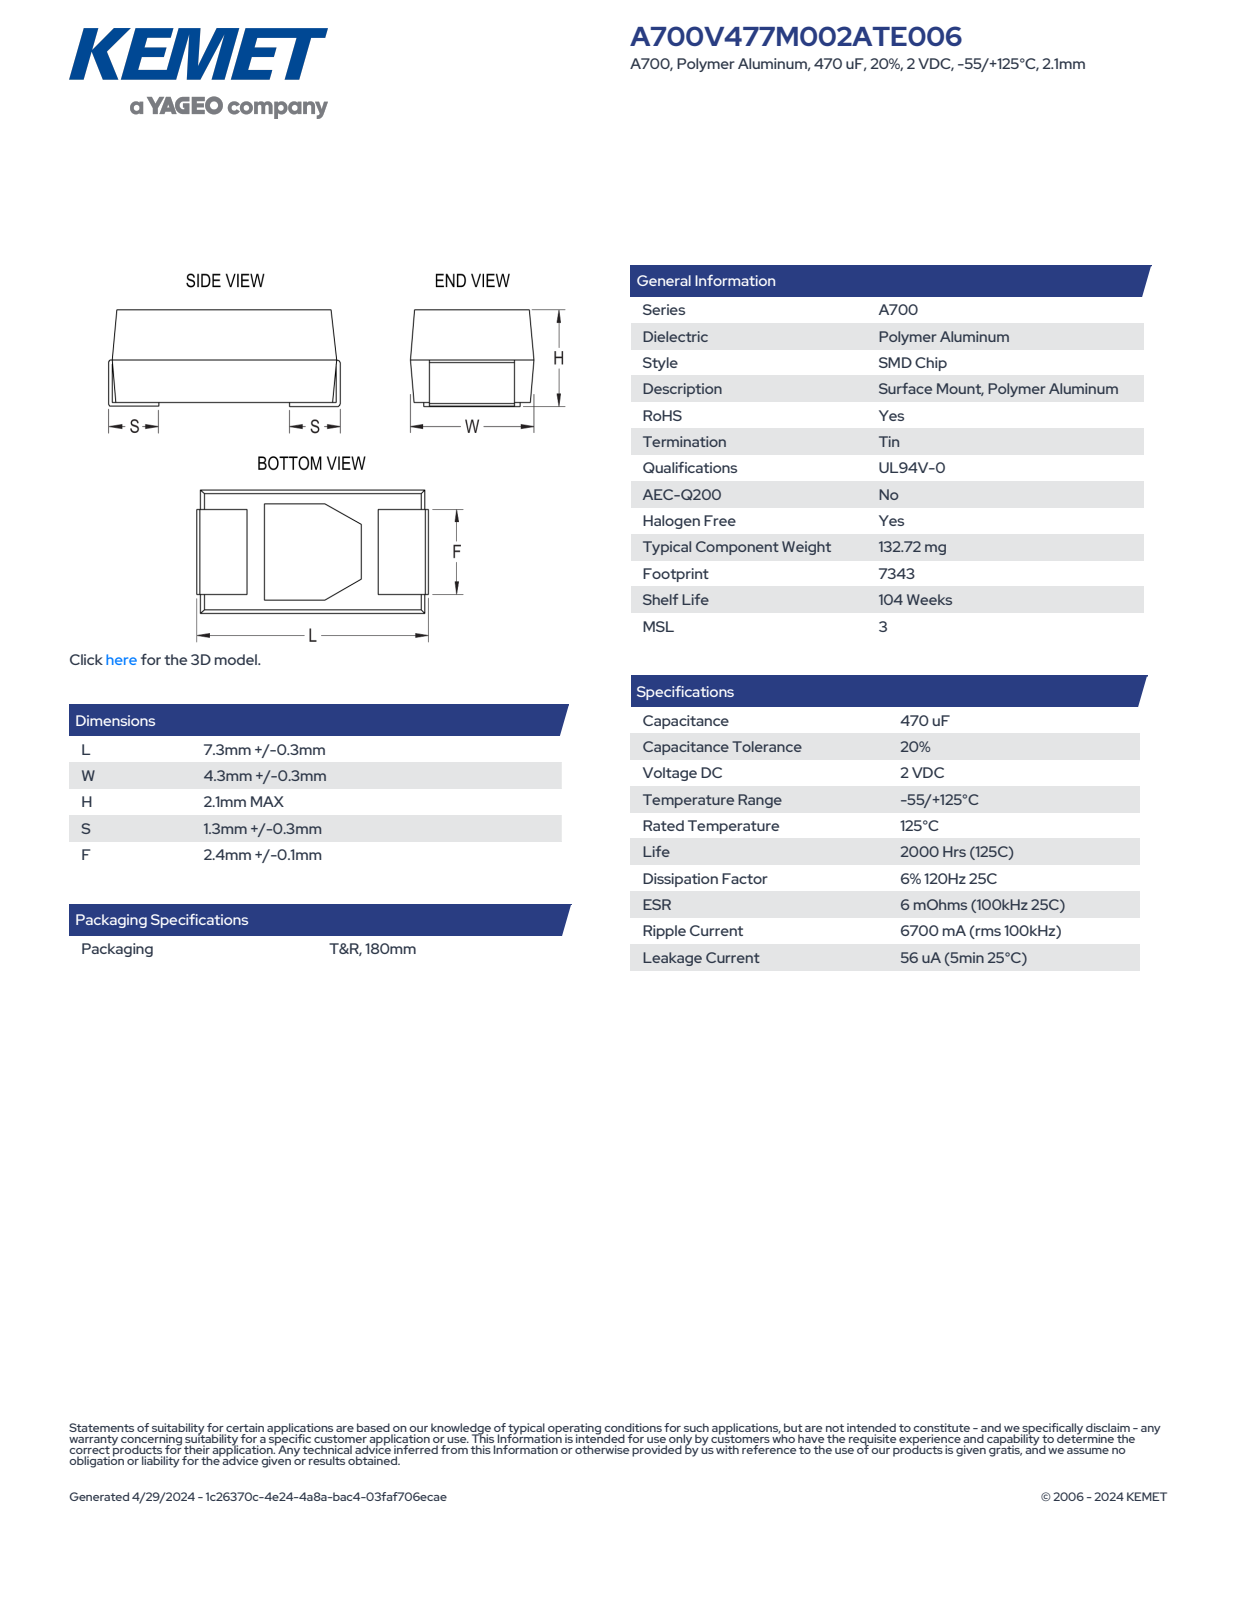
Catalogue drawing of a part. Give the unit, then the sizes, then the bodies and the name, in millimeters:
Units: millimetres
Overall size (bounding box): 7.6 × 4.6 × 2.1
Partial cylindrical surfaces — rounded edges, fillets, slot ends (radius × count): R0.1 ×4
Main face-to-face distances: 2, 2.1, 7.18, 4.52, 4.51, 7.5, 7.4, 7.6, 1.64, 5.96
Volume: 65 mm³ · Surface area: 123 mm²
Bodies: 1 solid, 82 faces (78 planar, 4 cylindrical, 0 other)
Part name (STEP PRODUCT): CAS_SMD_L7.6W4.6H2.1S1.3F2.5
STEP written by: SolidWorks 2021 (AUTOMOTIVE_DESIGN)
